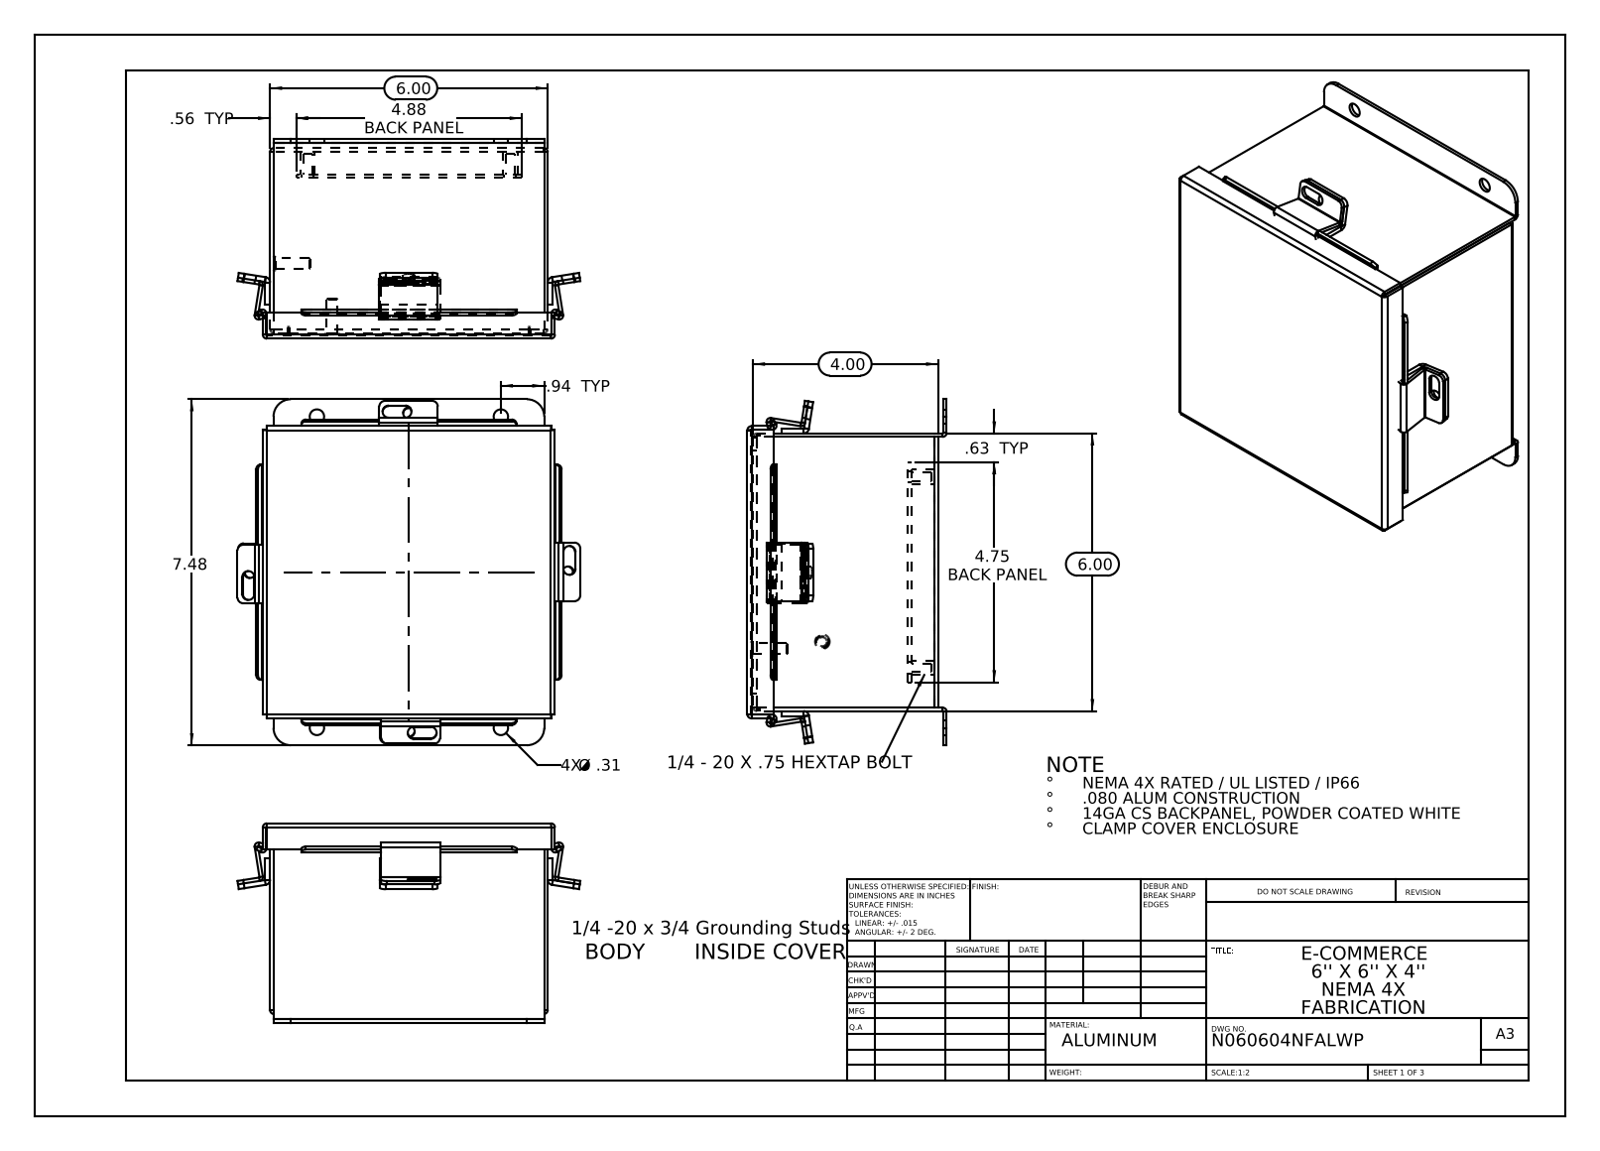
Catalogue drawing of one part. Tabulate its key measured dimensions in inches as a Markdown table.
| quantity | value |
| --- | --- |
| part name | N060604NFSSWP JIC Backpanel; N060604NFSSWP JIC Clamp Bracket; N060604NFSSWP JIC Bottom; N060604NFSSWP HW-CD-S-25020-034 (+6 more) |
| STEP written by | SolidWorks 2013 (CONFIG_CONTROL_DESIGN) |
| units | inches |
| bodies | 19 solids, 456 faces (292 planar, 144 cylindrical, 20 other) |
| overall size | 7.476 × 7.407 × 4.308 |
| volume | 17.78 in³ |
| surface area | 486.9 in² |
| round holes (diameter × count) | 0.25 × 8, 0.187 × 4, 0.312 × 4 |
| round bosses / shafts (diameter × count) | 0.313 × 4, 0.315 × 2, 0.236 × 2 |
| partial cylindrical surfaces (radius × count) | 0.009 × 16, 0.125 × 14, 0.013 × 12, 0.088 × 12, 0.083 × 8, 0.1 × 8, 0.133 × 8, 0.084 × 4 |
| main face-to-face distances | 0.075, 5.925, 4.046, 5.85, 6, 3.971, 4.121, 0.575, 0.5, 3.471 |
| hole center spacings | 1.315, 4.373, 5.43, 6.846, 3.976, 4.126, 4.375, 6.013 |
